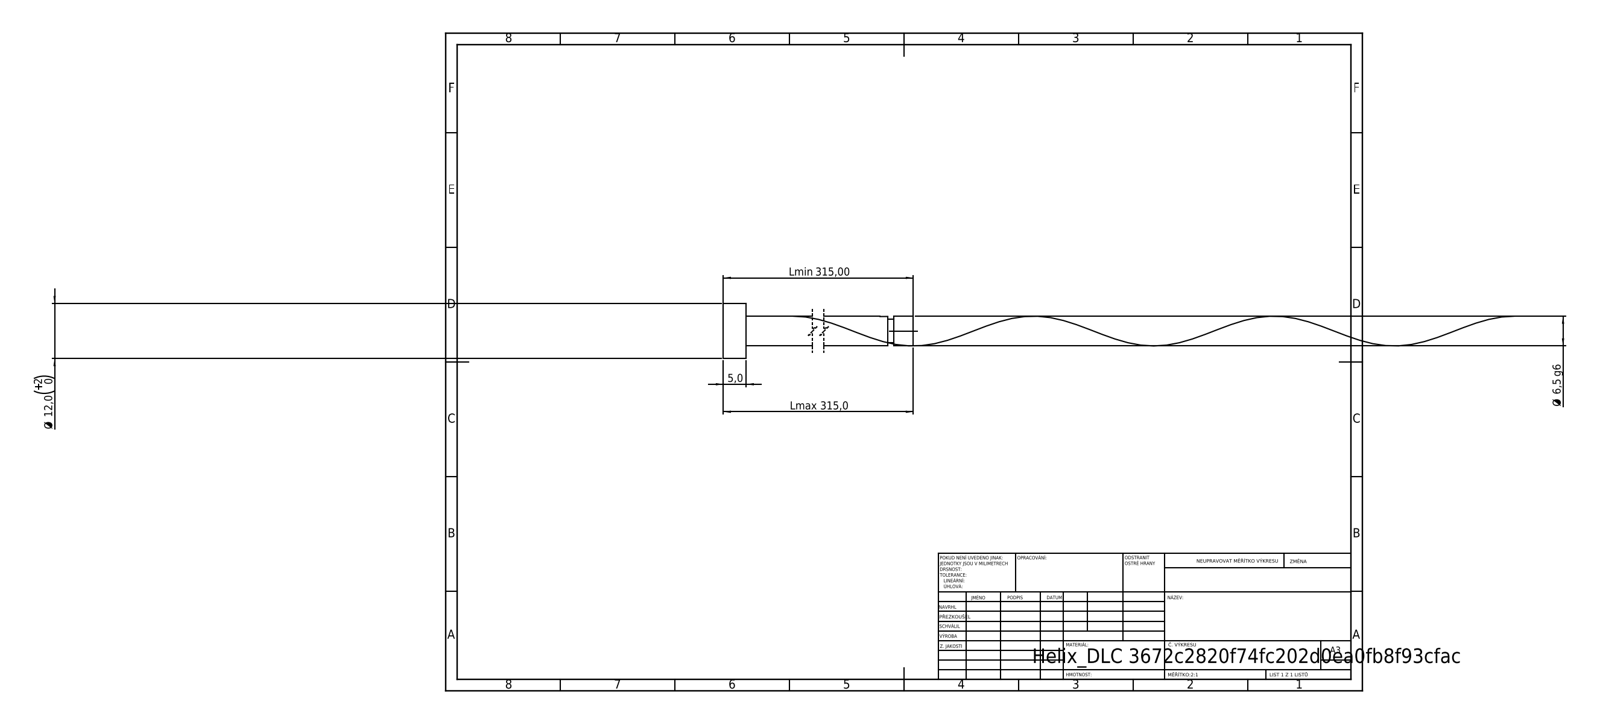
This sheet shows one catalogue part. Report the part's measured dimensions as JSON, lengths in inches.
{"step_written_by": "SolidWorks 2019 (CONFIG_CONTROL_DESIGN)", "units": "inches", "bodies": {"solids": 1, "faces": 21, "planar": 6, "cylindrical": 14, "other": 1}, "overall_size": [12.402, 0.472, 0.472], "volume_in3": 0.655, "surface_area_in2": 10.65, "round_bosses_or_shafts": [[0.472, 1], [0.256, 1], [0.205, 1]], "face_to_face_distances": [0.197, 12.402, 12.205, 12.233, 12.036, 0.169, 12.182, 11.985, 0.051, 0.22]}
